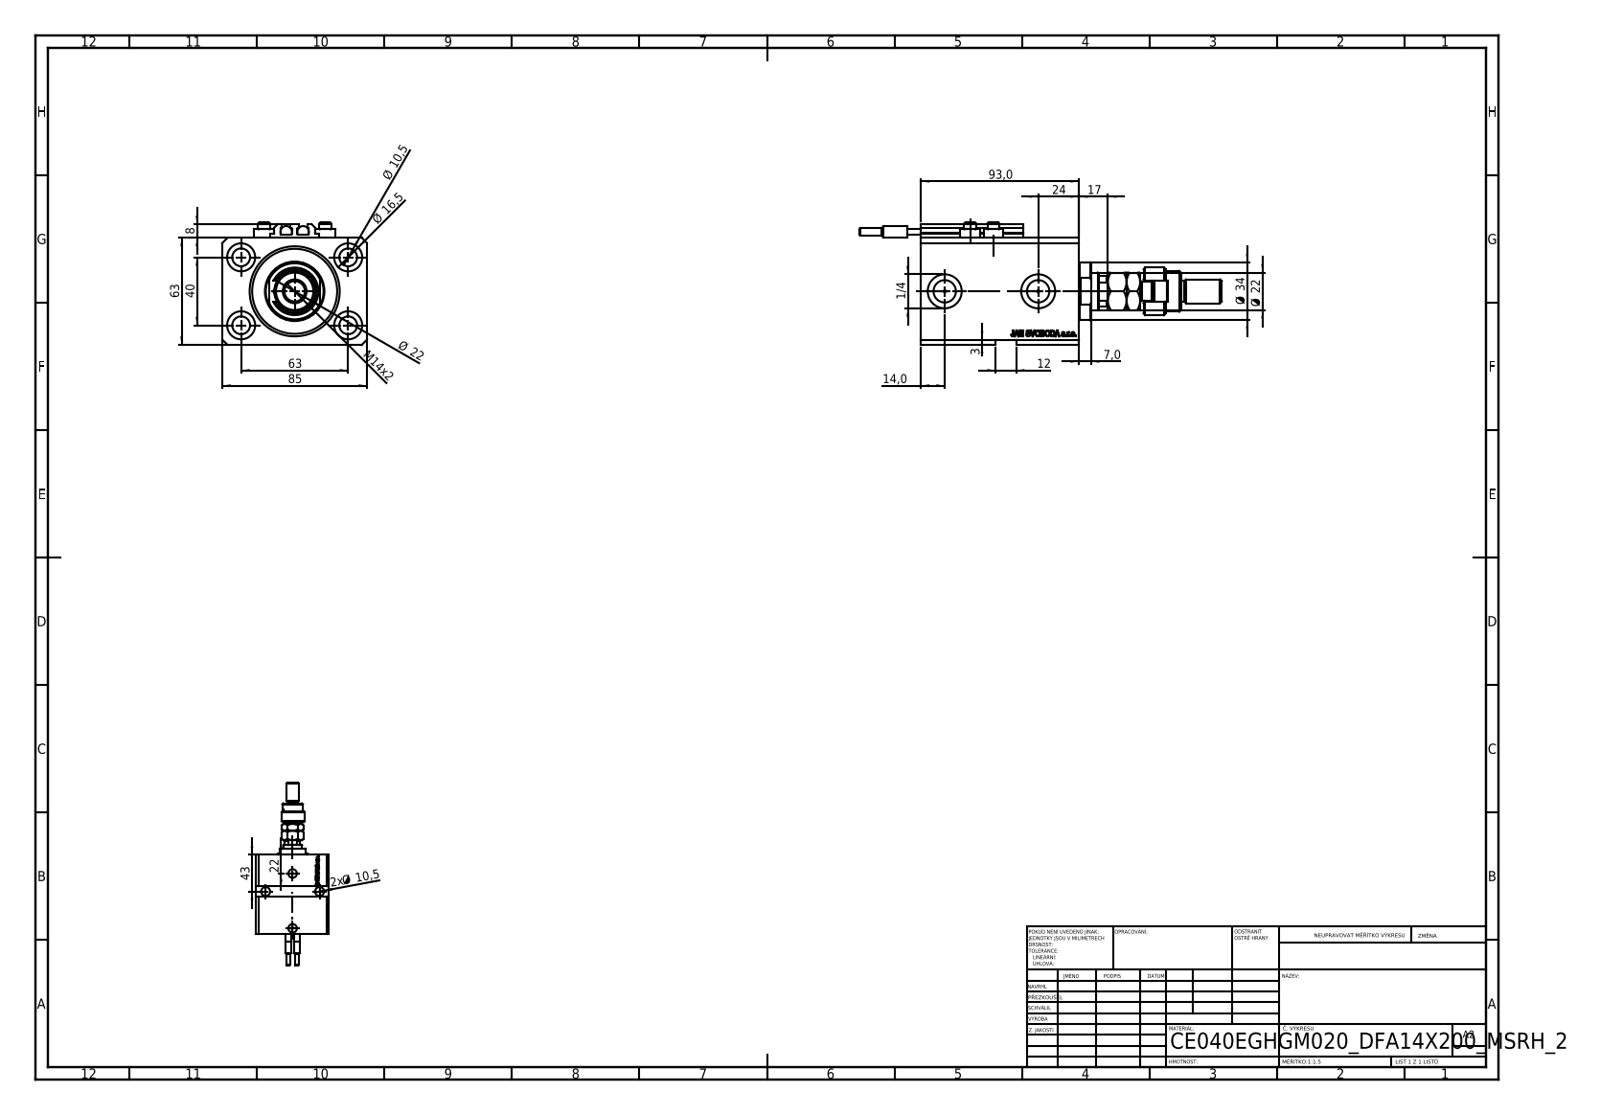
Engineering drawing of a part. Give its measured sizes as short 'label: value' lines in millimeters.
name: ALLEN BOLT V250CE; FEMALE_PART_FOR_DFA; V250CE_E_Body; MFA (+3 more)
written by: SolidWorks 2019 (CONFIG_CONTROL_DESIGN)
unit: mm
bodies: 12 solids, 1224 faces (595 planar, 151 cylindrical, 478 other)
size: 213 × 85 × 72
volume: 462 740 mm³; area: 106 498 mm²
holes: 6× ⌀10.5, 4× ⌀1.25, 4× ⌀4, 4× ⌀16.5, 2× ⌀10, 2× ⌀13.16, 2× ⌀20, 1× ⌀12.5, 1× ⌀22, 1× ⌀40, 1× ⌀53
bosses: 4× ⌀11.6, 4× ⌀7, 2× ⌀6.8, 2× ⌀6.5, 2× ⌀4, 1× ⌀34, 1× ⌀28, 1× ⌀24
rounds: 10× R0.2, 1× R9.75, 1× R10.5
face distances: 63, 85, 93, 17, 76, 3, 11.4, 64.6, 81.6, 65
hole spacings: 37.31, 63, 13.6, 15.4, 24.96, 28.02, 28.43, 33.62
